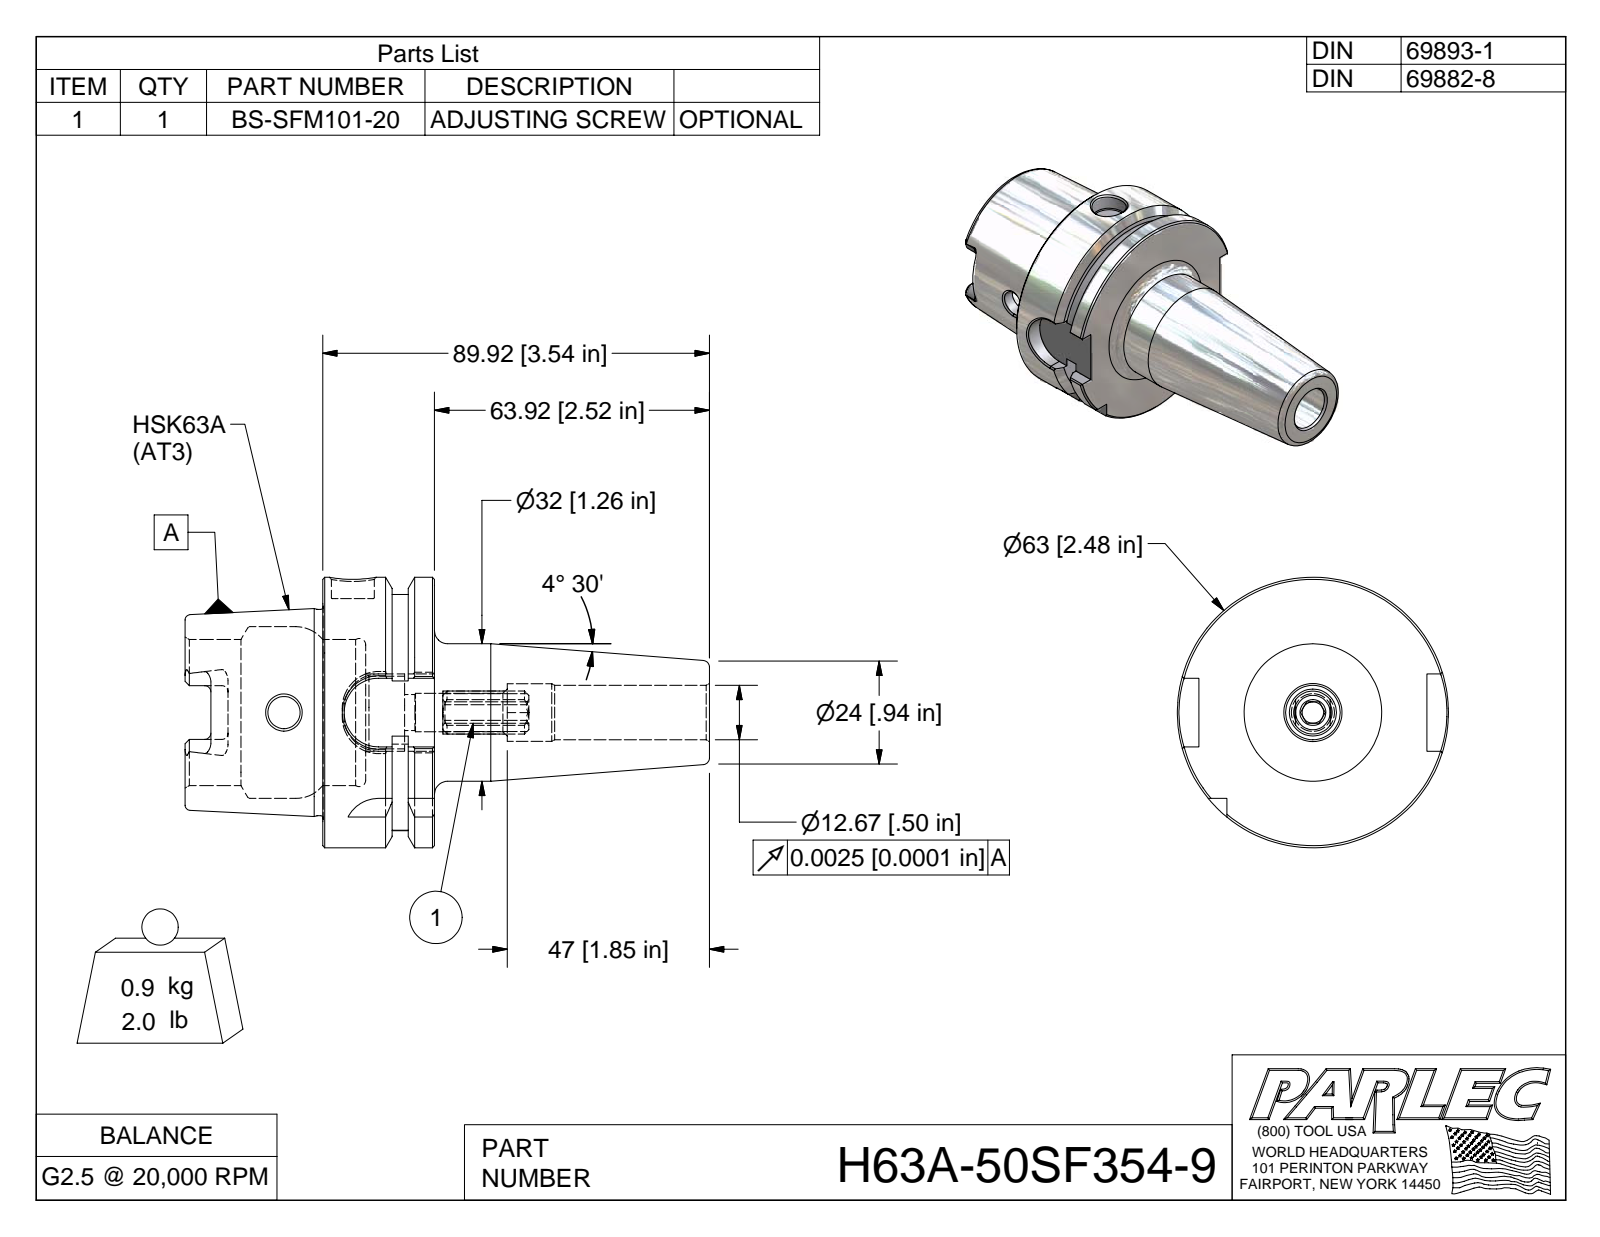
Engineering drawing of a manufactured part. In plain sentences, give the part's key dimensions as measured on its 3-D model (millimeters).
The part is named "H63A-50SF354-9; H63A-50SF354-9-1; BS-SFM101-20". Its 3-D file was written by "Autodesk Inventor 2009 (AUTOMOTIVE_DESIGN)". It is 2 solids with 157 faces: 58 planar, 35 cylindrical and 64 other. Overall it measures 121.9 by 63 by 63 millimeters. Its volume is 117 700 cubic millimeters and its surface area 30 940 square millimeters. Round holes: 1 of diameter 7.5, 1 of diameter 10, 1 of diameter 12.7, 1 of diameter 13.4, 1 of diameter 16.9, 1 of diameter 34, 1 of diameter 40. Round bosses or shafts: 1 of diameter 63, 1 of diameter 48, 1 of diameter 32. Partial cylindrical surfaces (rounded edges, fillets, slot ends): 6 of radius 1.5, 4 of radius 2.9, 4 of radius 8, 1 of radius 5, 1 of radius 27.5. The main face-to-face distances are 26, 6.1, 9.9, 16, 10, 32, 42, 58, 3.8, 48.1.
